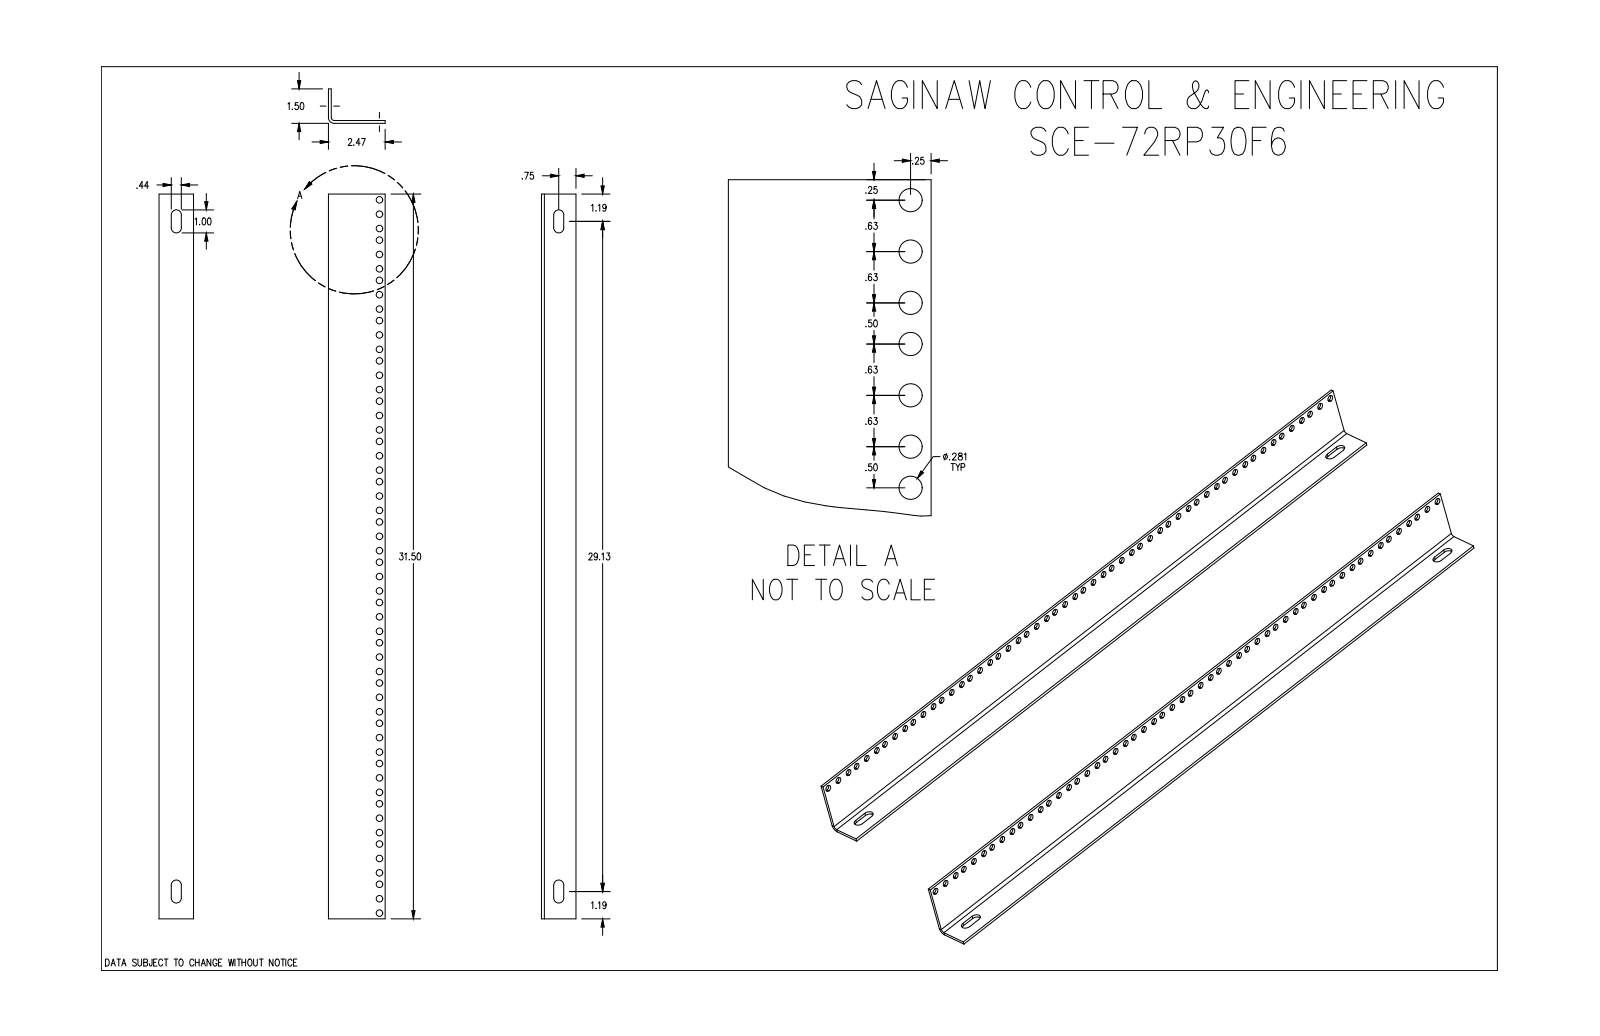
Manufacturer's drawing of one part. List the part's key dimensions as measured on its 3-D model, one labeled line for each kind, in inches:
Part name (STEP PRODUCT): SCE-72RP30F6
STEP written by: SolidWorks 2019 (CONFIG_CONTROL_DESIGN)
Units: inches
Bodies: 1 solid, 130 faces (16 planar, 114 cylindrical, 0 other)
Overall size (bounding box): 31.5 × 2.469 × 1.5
Volume: 14.3 in³ · Surface area: 244.2 in²
Round holes (diameter × count): ⌀0.281 ×54
Partial cylindrical surfaces — rounded edges, fillets, slot ends (radius × count): R0.219 ×4, R0.125 ×1, R0.25 ×1
Main face-to-face distances: 0.125, 2.469, 2.344, 1.5, 1.375, 31.5, 0.531, 0.969, 0.407, 0.844
Hole centre spacings: 1.75, 3.5, 5.25, 7, 8.75, 0.625, 0.625, 1.25
